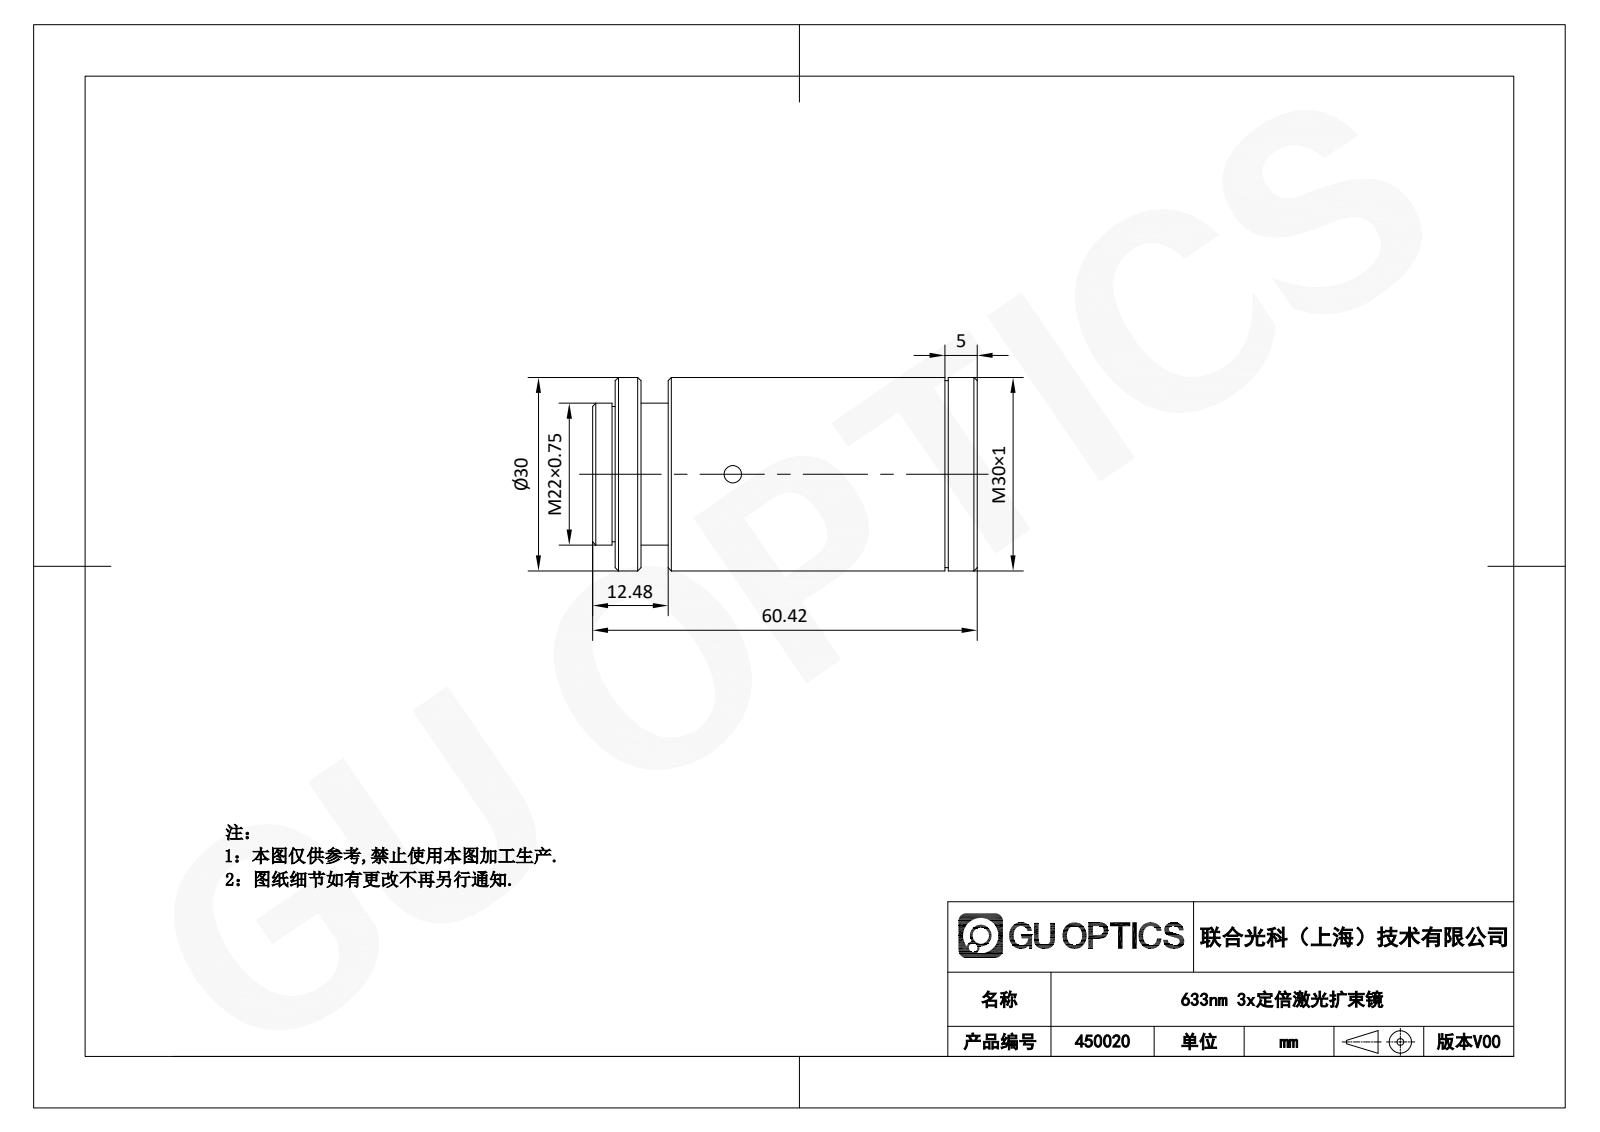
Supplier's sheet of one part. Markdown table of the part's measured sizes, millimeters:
| quantity | value |
| --- | --- |
| part name | 450020 |
| STEP written by | SolidWorks 2020 (CONFIG_CONTROL_DESIGN) |
| units | millimeters |
| bodies | 1 solid, 44 faces (12 planar, 22 cylindrical, 10 other) |
| overall size | 60.42 × 30 × 30 |
| volume | 38 922 mm³ |
| surface area | 8 396 mm² |
| round holes (diameter × count) | 2 × 1, 8 × 1, 18 × 1, 20 × 1 |
| round bosses / shafts (diameter × count) | 30 × 1, 29 × 1, 22 × 1, 21 × 1 |
| main face-to-face distances | 2, 58.42, 1, 1.5, 56.92, 52.92, 2.5, 54.92, 3.5, 60.42 |
